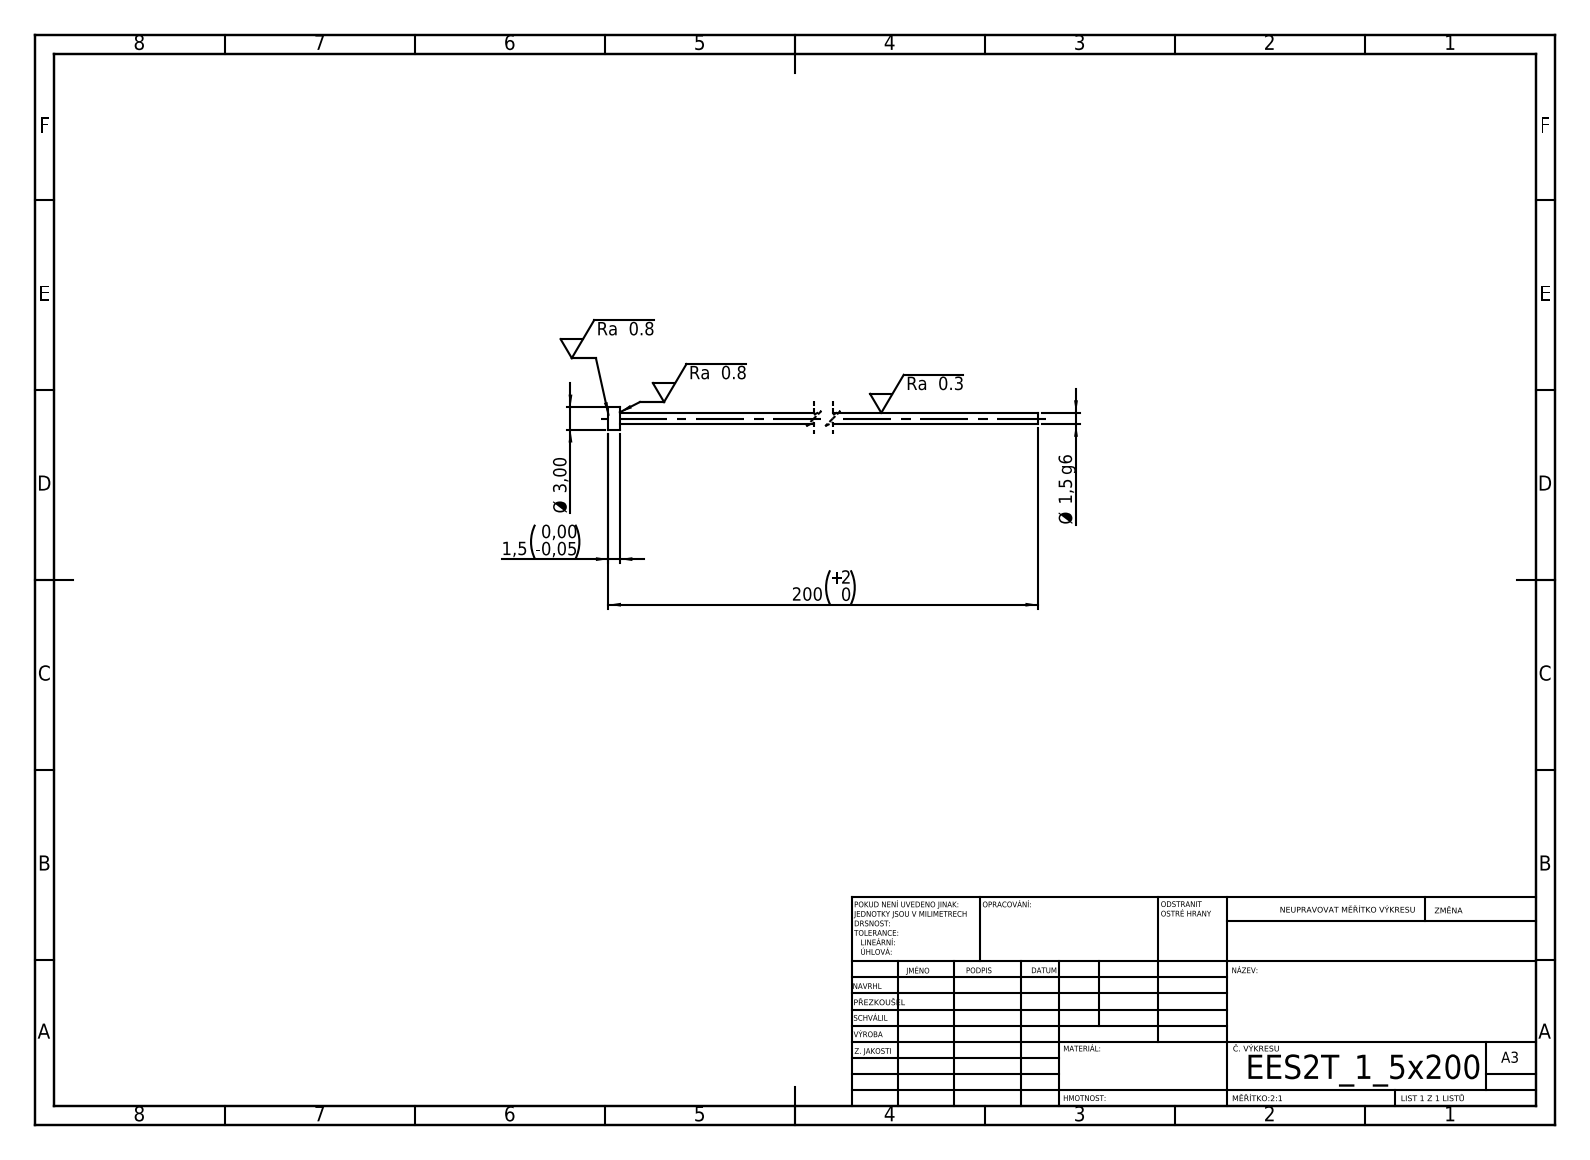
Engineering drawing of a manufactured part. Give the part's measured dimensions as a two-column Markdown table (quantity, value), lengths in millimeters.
| quantity | value |
| --- | --- |
| STEP written by | SolidWorks 2019 (CONFIG_CONTROL_DESIGN) |
| units | millimeters |
| bodies | 1 solid, 7 faces (3 planar, 4 cylindrical, 0 other) |
| overall size | 200 × 3 × 3 |
| volume | 361 mm³ |
| surface area | 964 mm² |
| round bosses / shafts (diameter × count) | 3 × 1, 1.5 × 1 |
| main face-to-face distances | 1.5, 200, 198.5 |
